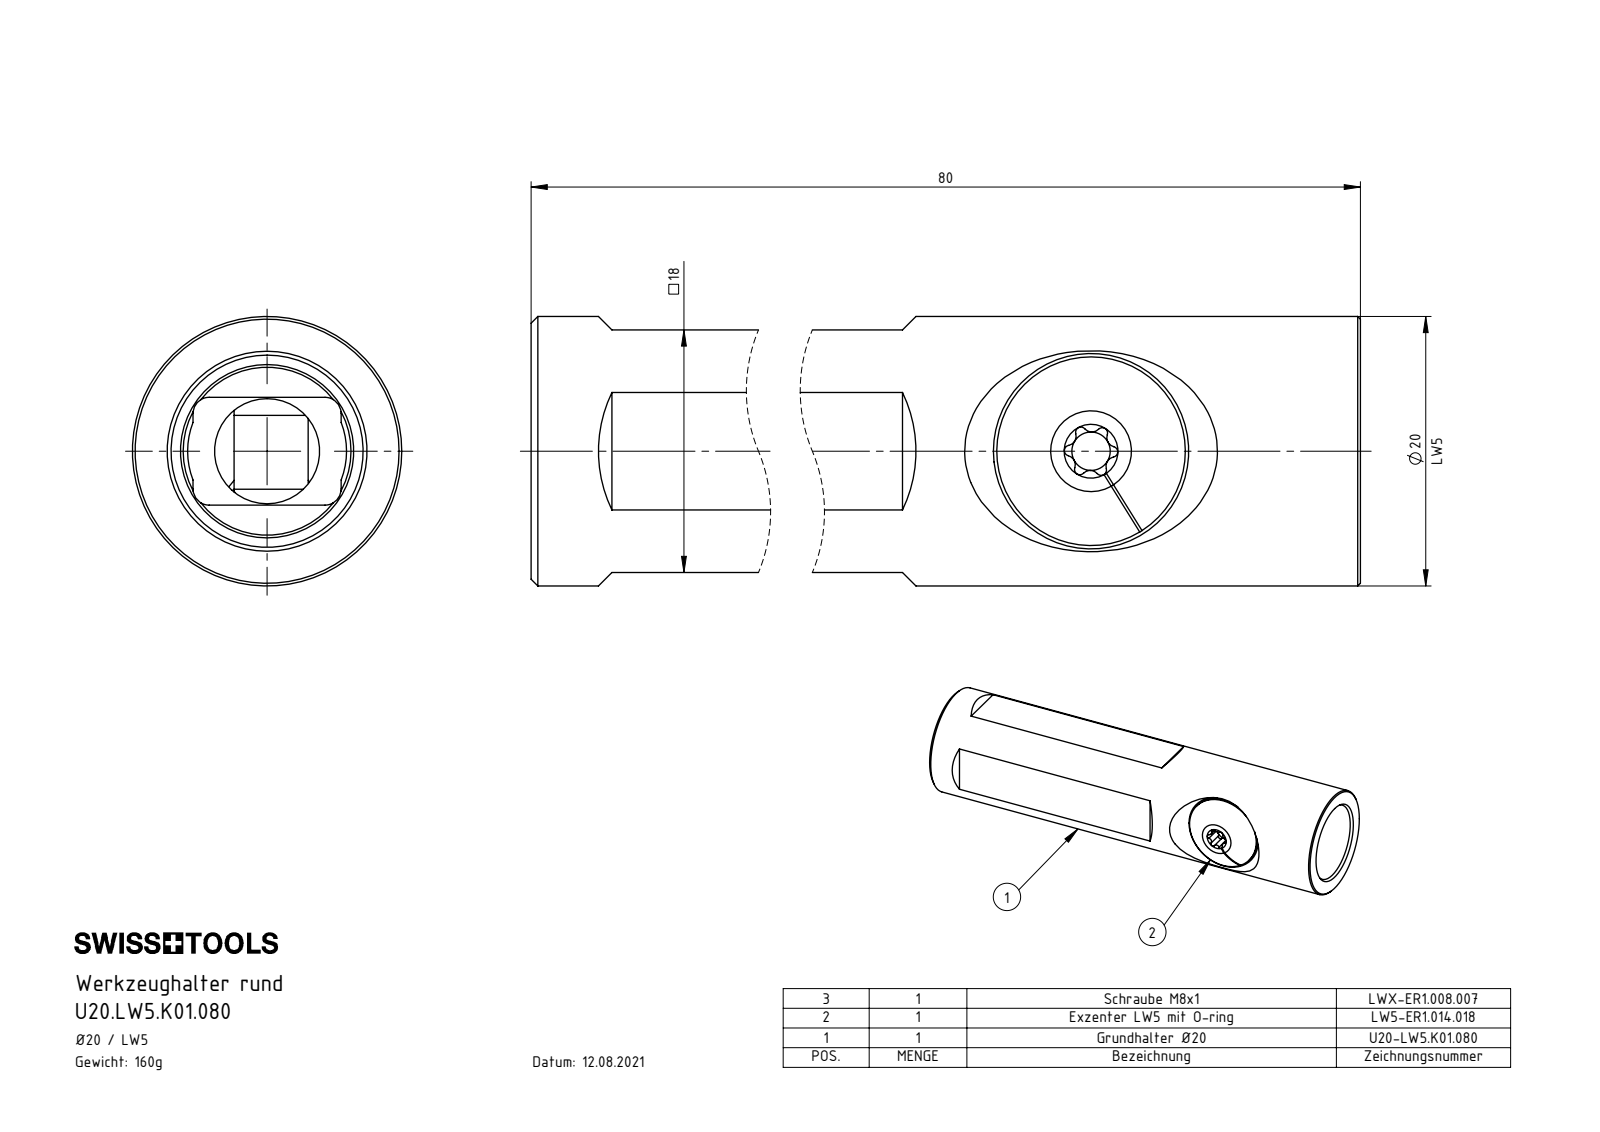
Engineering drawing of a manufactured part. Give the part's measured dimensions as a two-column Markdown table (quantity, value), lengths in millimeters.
| quantity | value |
| --- | --- |
| part name | U20.LW5.K01.080; LW5-ER1.014.018; DIN 3771 - 10x1; LW5-ER1.014.018_A_Standard<Wie bearbeitet> (+1 more) |
| STEP written by | SolidWorks 2017 (AUTOMOTIVE_DESIGN) |
| units | millimeters |
| bodies | 4 solids, 130 faces (53 planar, 42 cylindrical, 35 other) |
| overall size | 80 × 20 × 20 |
| volume | 19 234 mm³ |
| surface area | 8 918 mm² |
| round holes (diameter × count) | 1 × 1, 2.85 × 1, 7 × 1, 7.8 × 1, 12.86 × 1 |
| round bosses / shafts (diameter × count) | 20 × 1, 14 × 1, 12 × 1, 10.2 × 1 |
| partial cylindrical surfaces (radius × count) | 0.4 × 6, 0.69 × 6, 1.2 × 4, 2.75 × 2, 4.15 × 2, 4.1 × 1, 4.7 × 1, 5.9 × 1 |
| main face-to-face distances | 18, 80, 15.3, 2.7, 0.7, 14.6, 17.3, 12.1, 13.2, 1.4 |
